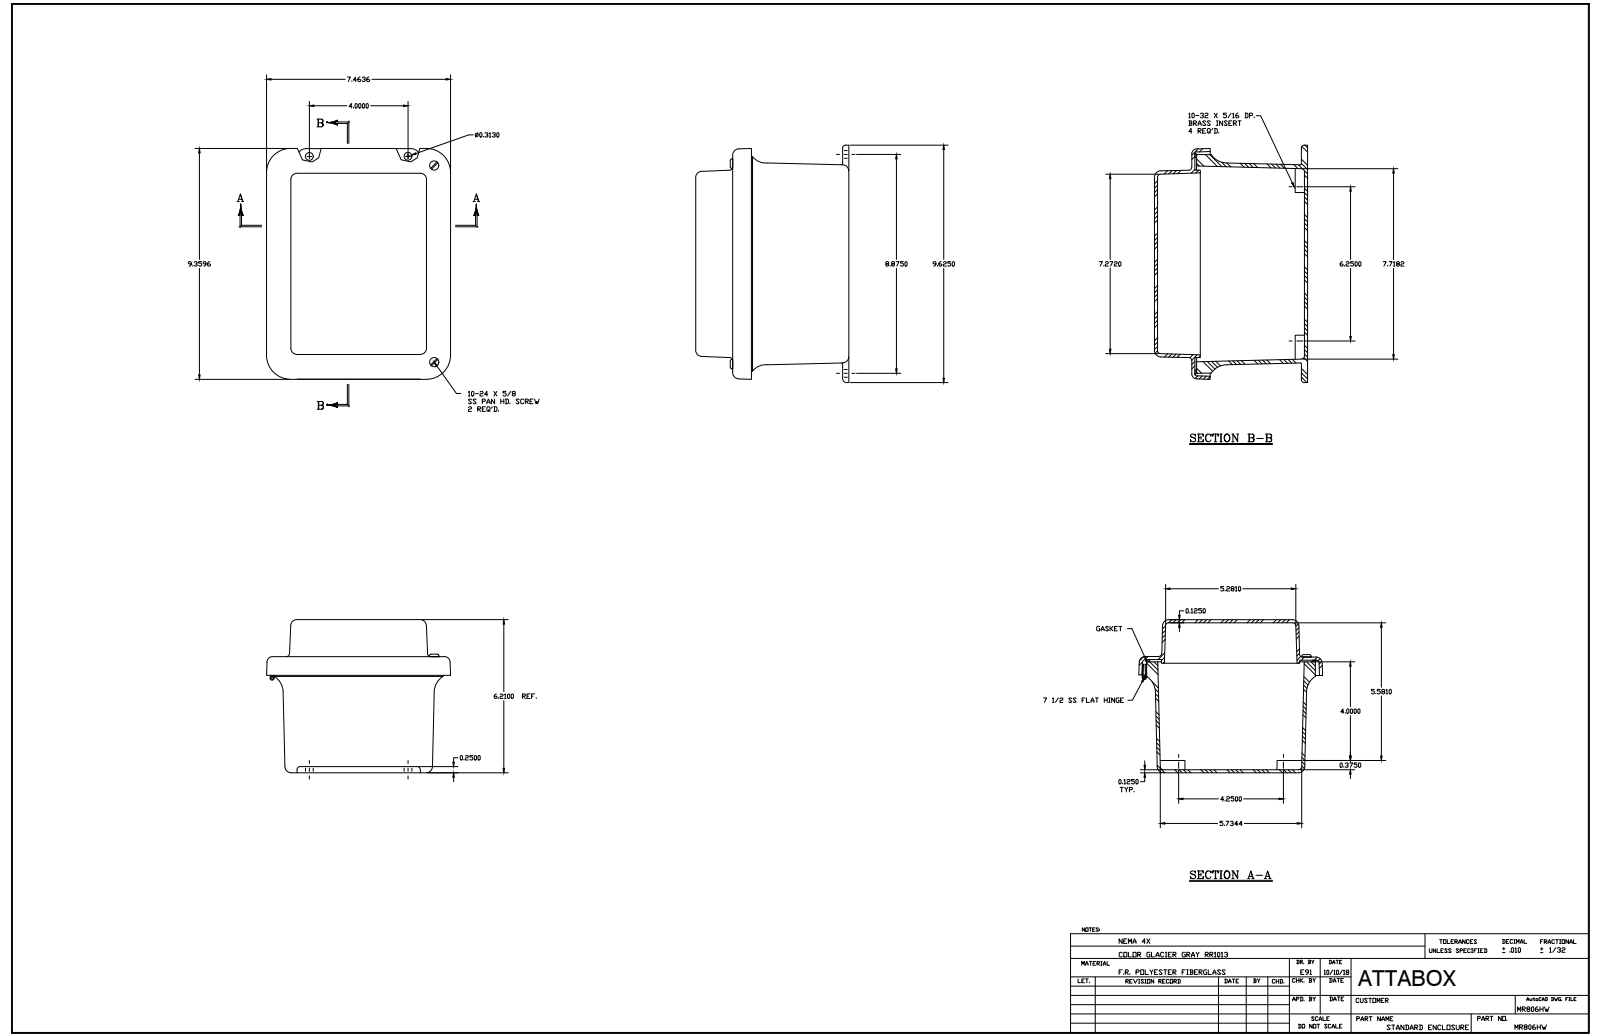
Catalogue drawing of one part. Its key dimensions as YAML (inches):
part_name: "MR806HW"
step_written_by: "SolidWorks 2018 (AUTOMOTIVE_DESIGN)"
units: inches
bodies: {solids: 19, faces: 763, planar: 252, cylindrical: 281, other: 230}
overall_size: [9.625, 7.492, 6.215]
volume: 48.38
surface_area: 674.9
round_holes:
  - {diameter: 0.131, count: 6}
  - {diameter: 0.14, count: 6}
  - {diameter: 0.152, count: 5}
  - {diameter: 0.156, count: 4}
  - {diameter: 0.218, count: 4}
  - {diameter: 0.145, count: 2}
  - {diameter: 0.085, count: 1}
  - {diameter: 0.085, count: 1}
round_bosses_or_shafts:
  - {diameter: 0.27, count: 6}
  - {diameter: 0.25, count: 5}
  - {diameter: 0.125, count: 3}
  - {diameter: 0.19, count: 2}
  - {diameter: 0.156, count: 2}
  - {diameter: 0.125, count: 2}
  - {diameter: 0.155, count: 1}
partial_cylinders:
  - {radius: 0.031, count: 20}
  - {radius: 0.125, count: 20}
  - {radius: 0.25, count: 12}
  - {radius: 0.2, count: 4}
  - {radius: 0.31, count: 4}
  - {radius: 0.313, count: 4}
  - {radius: 0.375, count: 4}
  - {radius: 0.767, count: 4}
face_to_face_distances: [0.125, 0.125, 1.515, 5.965, 4.45, 6.09, 6.215, 6.089, 4.575, 1.64]
hole_center_spacings: [3.5, 1.326, 5.271, 7.249, 8.864, 0.25, 3.25, 3]
